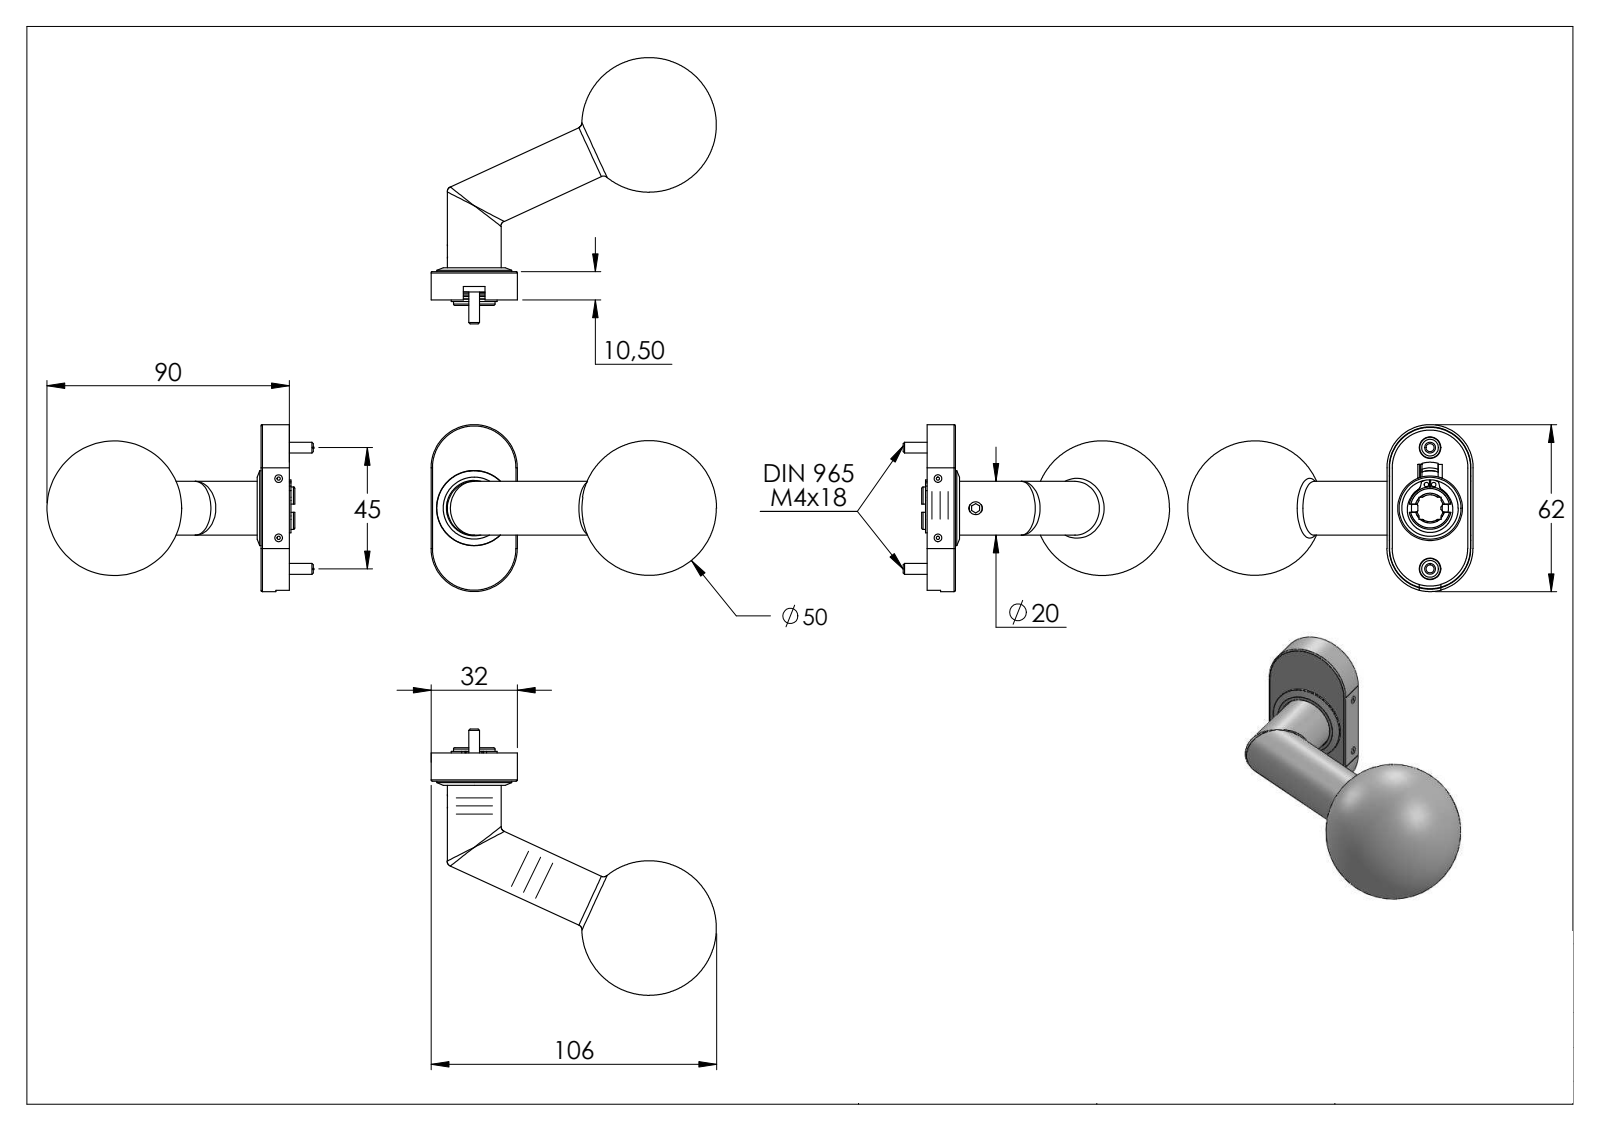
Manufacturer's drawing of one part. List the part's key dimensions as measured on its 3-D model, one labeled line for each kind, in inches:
Part name (STEP PRODUCT): 212-VA-D Teil1_212-VA-D Teil1; 212-VA-D; DIN 965; DIN 471 Wellensicherungsring (+8 more)
STEP written by: SolidWorks 2015 (CONFIG_CONTROL_DESIGN)
Units: inches
Bodies: 13 solids, 441 faces (243 planar, 77 cylindrical, 121 other)
Overall size (bounding box): 4.173 × 3.894 × 2.441
Volume: 2.108 in³ · Surface area: 63.57 in²
Round holes (diameter × count): ⌀0.067 ×2, ⌀0.244 ×2, ⌀0.197 ×1, ⌀0.543 ×1, ⌀0.618 ×1, ⌀0.63 ×1, ⌀0.642 ×1, ⌀0.665 ×1, ⌀0.75 ×1, ⌀0.811 ×1, ⌀1.102 ×1
Round bosses / shafts (diameter × count): ⌀0.787 ×2, ⌀0.304 ×2, ⌀0.283 ×2, ⌀0.157 ×2, ⌀0.142 ×2, ⌀1.094 ×1, ⌀0.945 ×1, ⌀0.823 ×1
Partial cylindrical surfaces — rounded edges, fillets, slot ends (radius × count): R0.02 ×12, R0.031 ×4, R0.03 ×2, R0.098 ×2, R0.272 ×2, R0.315 ×2, R0.551 ×2, R0.591 ×2
Main face-to-face distances: 0.039, 0.035, 0.059, 0.024, 0.098, 0.063, 0.079, 1.181, 0.378, 0.265
Hole centre spacings: 0.35, 0.543, 0.886, 1.233, 0.106, 1.772
